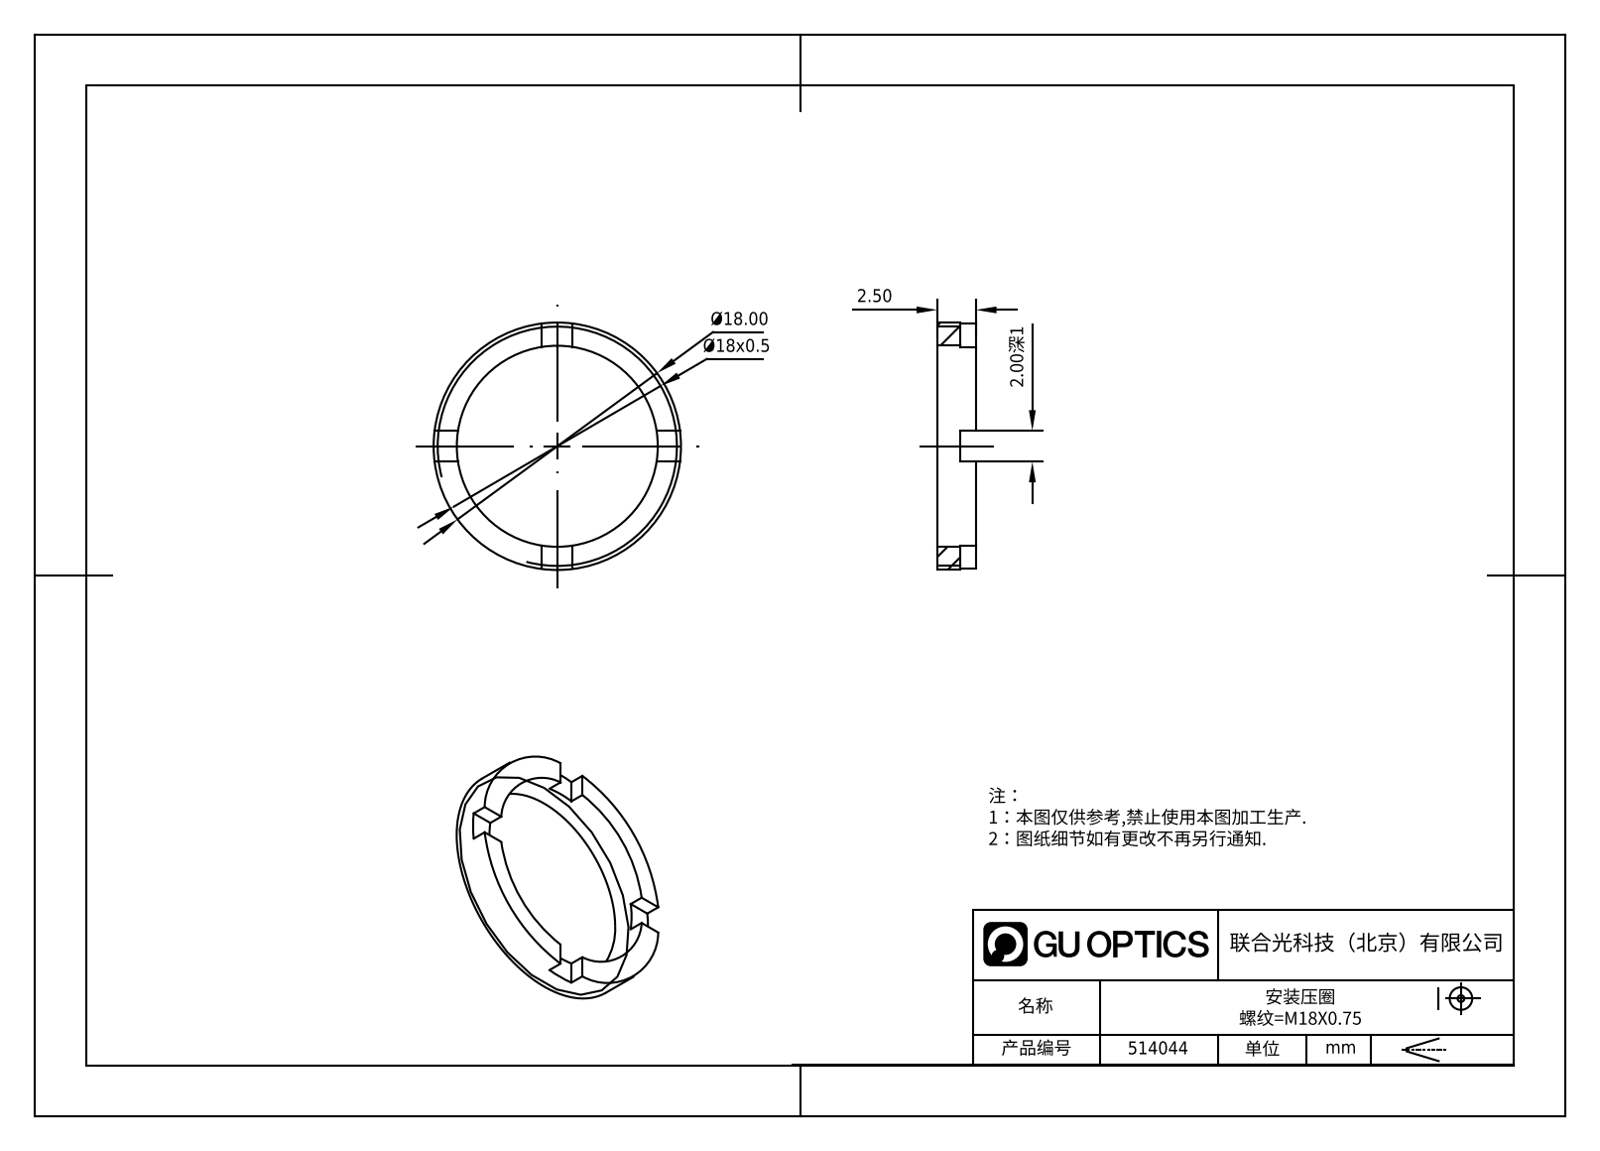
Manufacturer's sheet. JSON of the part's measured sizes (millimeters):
{"part_name": "514044", "step_written_by": "SolidWorks 2020 (CONFIG_CONTROL_DESIGN)", "units": "millimeters", "bodies": {"solids": 1, "faces": 21, "planar": 17, "cylindrical": 4, "other": 0}, "overall_size": [18, 18, 2.5], "volume_mm3": 182, "surface_area_mm2": 411, "round_holes": [[15, 1]], "round_bosses_or_shafts": [[18, 1]], "face_to_face_distances": [2.5, 1.5, 1, 2]}
